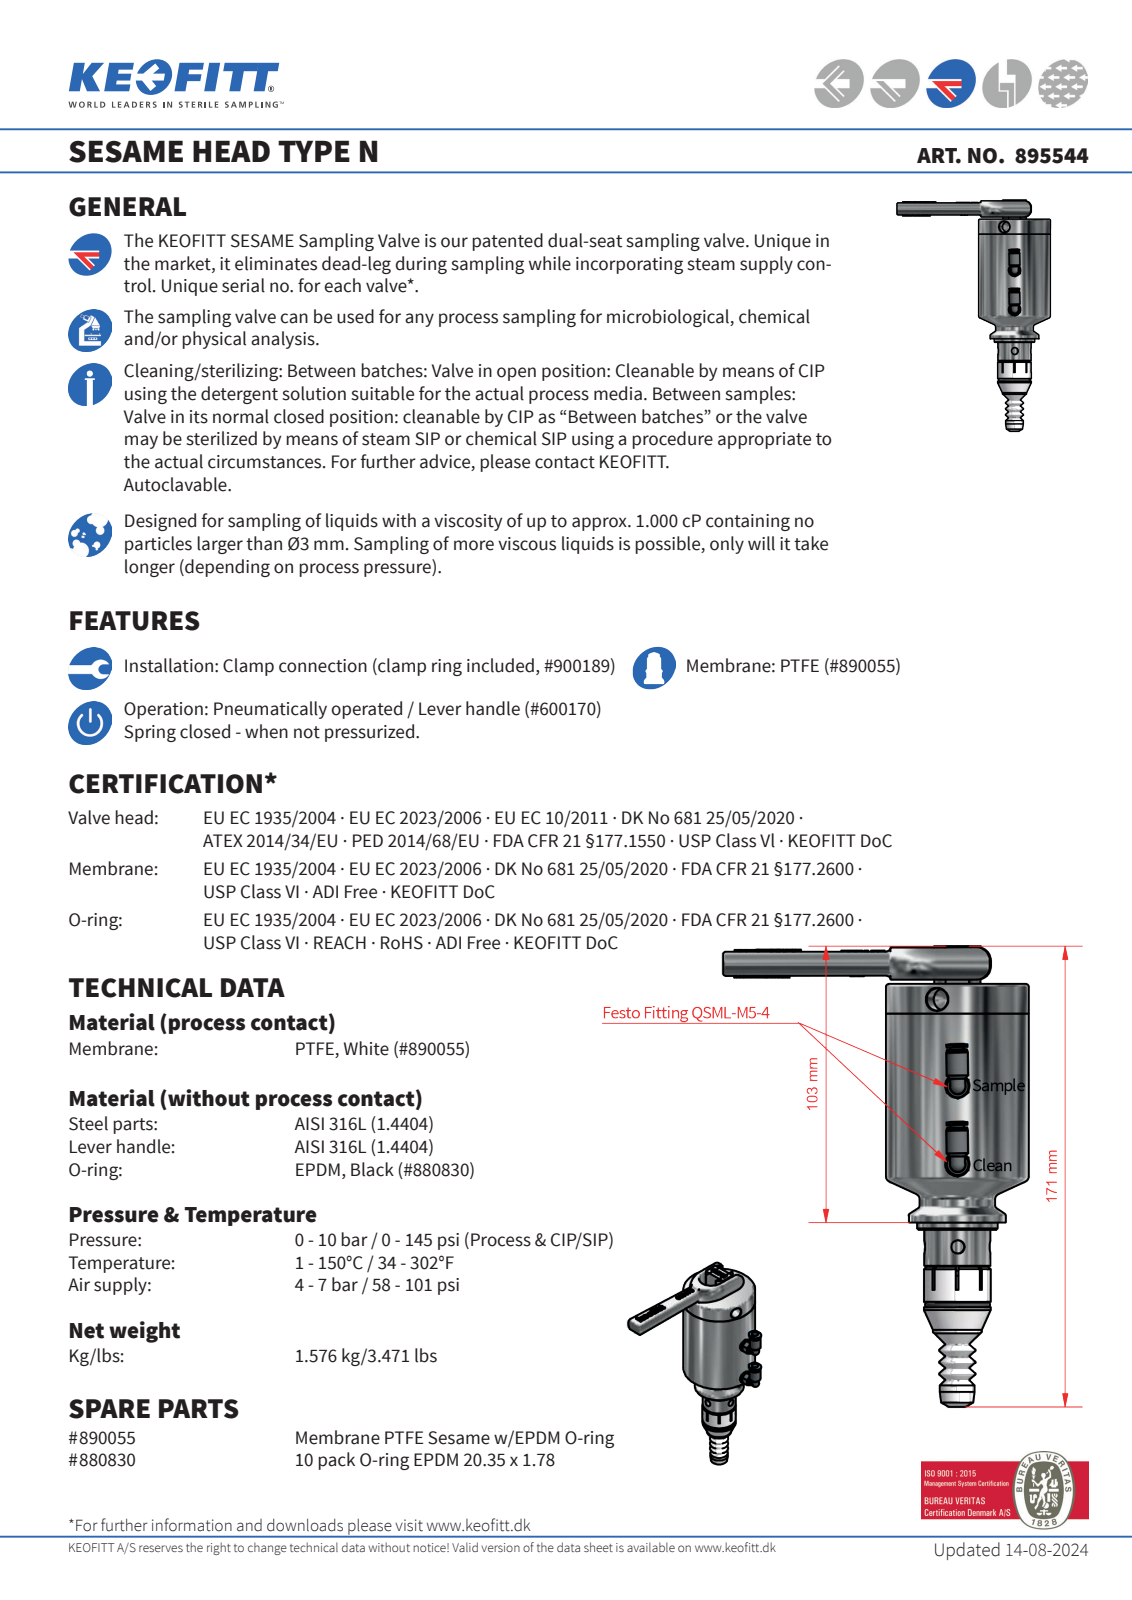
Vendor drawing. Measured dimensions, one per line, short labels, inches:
name: 895544_test asm simplify
written by: Autodesk Inventor 2022 (AUTOMOTIVE_DESIGN)
unit: in
bodies: 1 solid, 874 faces (336 planar, 159 cylindrical, 379 other)
size: 6.714 × 4.872 × 2.087
volume: 13.59 in³; area: 59.39 in²
holes: 2× ⌀0.157, 1× ⌀0.709
bosses: 4× ⌀0.22, 3× ⌀0.315, 3× ⌀0.236, 2× ⌀0.299, 2× ⌀0.291, 2× ⌀0.291, 2× ⌀0.246, 2× ⌀0.197
rounds: 41× R0.039, 14× R0.02, 4× R0.059, 4× R0.128, 4× R0.154, 3× R0.197, 2× R0.079, 1× R0.226
face distances: 0.315, 0.472, 0.157, 0.63, 0.059, 0.413, 0.445, 0.091, 0.354, 0.031
hole spacings: 1.142
